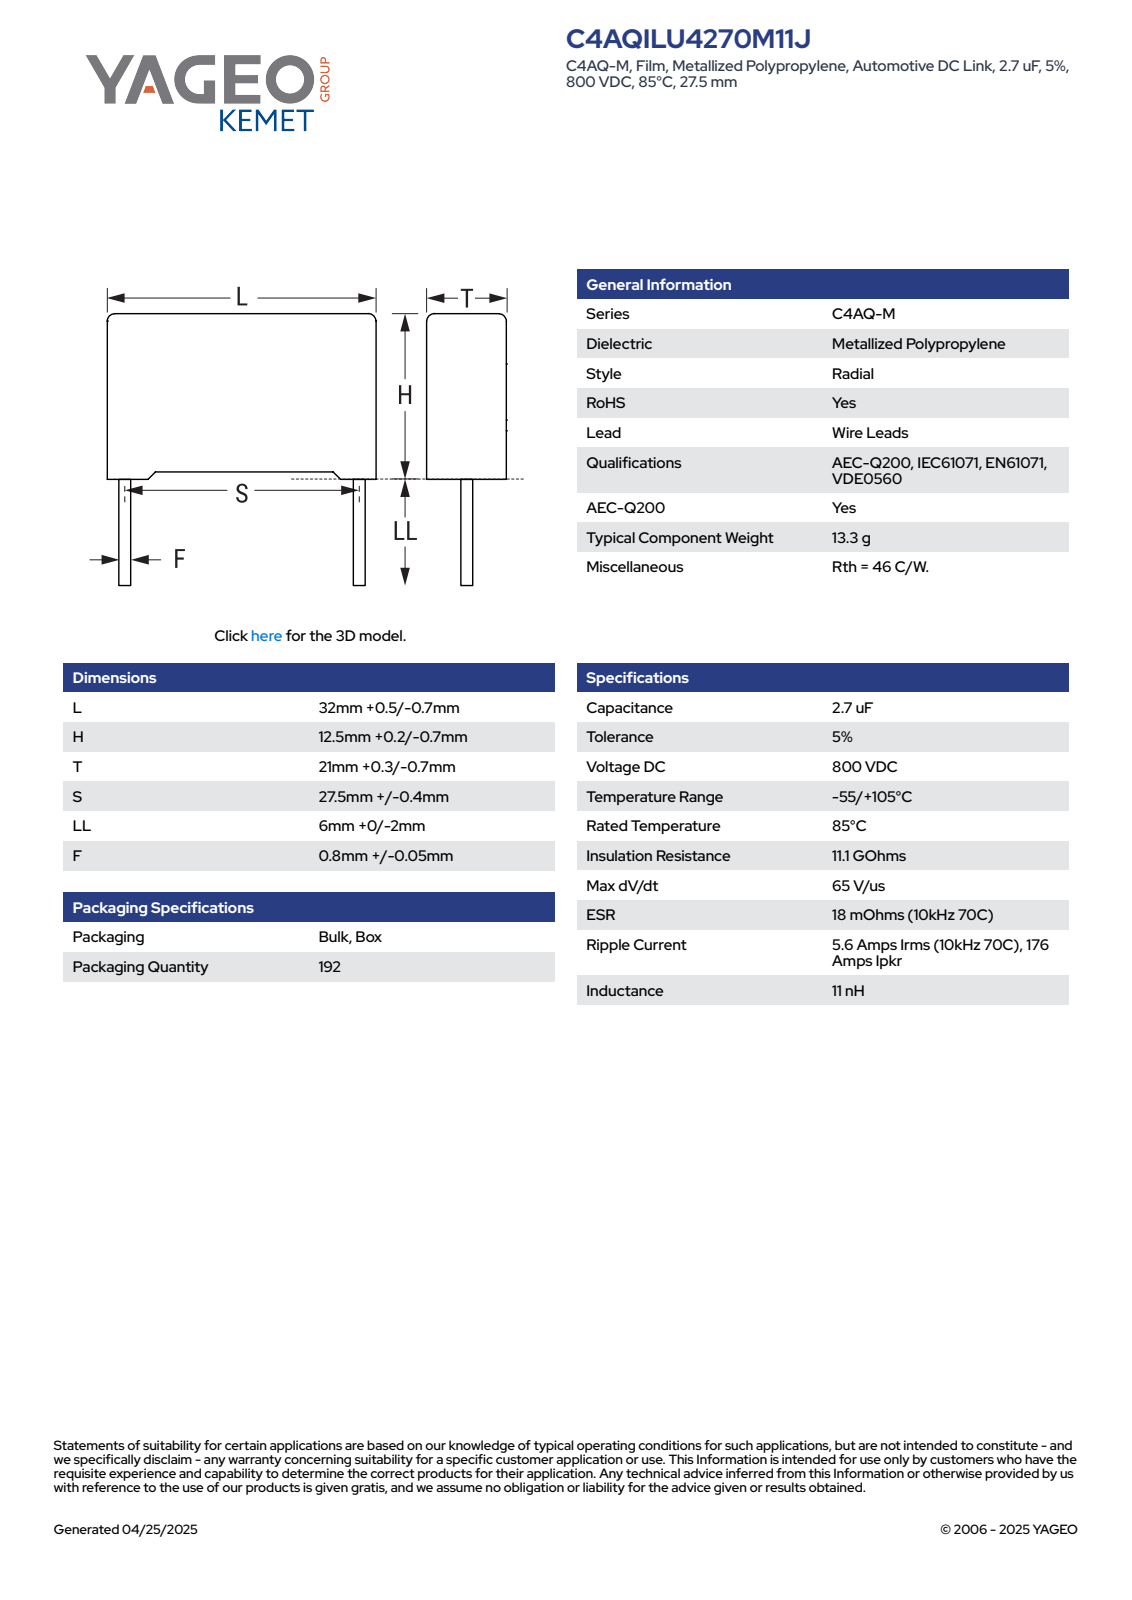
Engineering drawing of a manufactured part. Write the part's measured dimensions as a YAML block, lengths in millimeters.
part_name: "CFR_RB2CFP_32X12.5X21_L32.5H12.7T21.3S27.5LL6F0.85"
step_written_by: "SolidWorks 2014 (AUTOMOTIVE_DESIGN)"
units: millimeters
bodies: {solids: 4, faces: 85, planar: 77, cylindrical: 8, other: 0}
overall_size: [32.5, 21.3, 18.7]
volume: 8336
surface_area: 2876
round_bosses_or_shafts:
  - {diameter: 0.85, count: 2}
partial_cylinders:
  - {radius: 0.5, count: 4}
face_to_face_distances: [11.95, 21.3, 32.5, 0.75, 12.7, 1.08, 0.44, 0.31, 12.26, 31.42]
